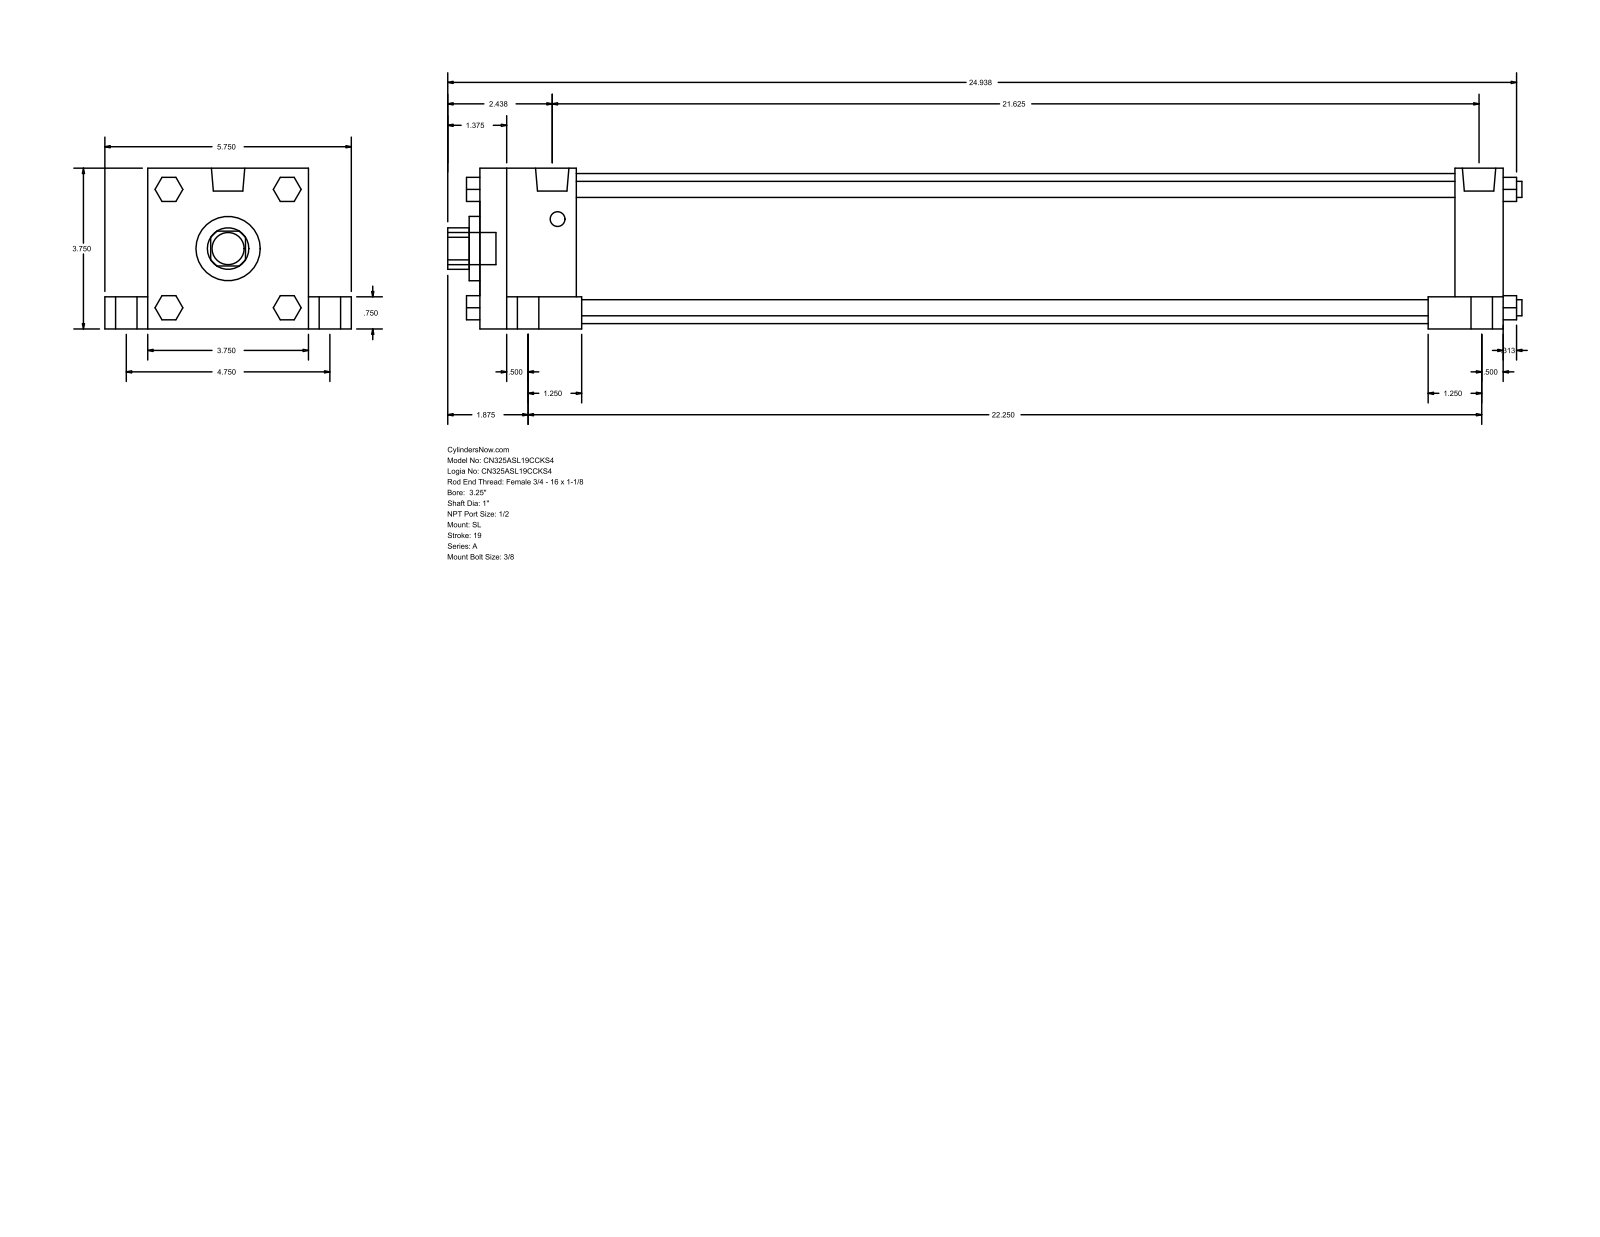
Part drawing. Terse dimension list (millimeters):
name: A_SL__0325_1
written by: GSSL Pune (CONFIG_CONTROL_DESIGN)
unit: mm
bodies: 0 solids, 150 faces (114 planar, 36 cylindrical, 0 other)
size: 636.59 × 146.05 × 95.25
holes: 1× ⌀25.4, 1× ⌀38.1, 1× ⌀88.9
bosses: 5× ⌀19.05, 4× ⌀12.7, 4× ⌀9.53, 4× ⌀8.73, 2× ⌀19.77
rounds: 1× R12.29
face distances: 95.24, 606.43, 19.05, 25.41, 120.65, 76.19, 57.15, 577.85, 520.7, 549.28
